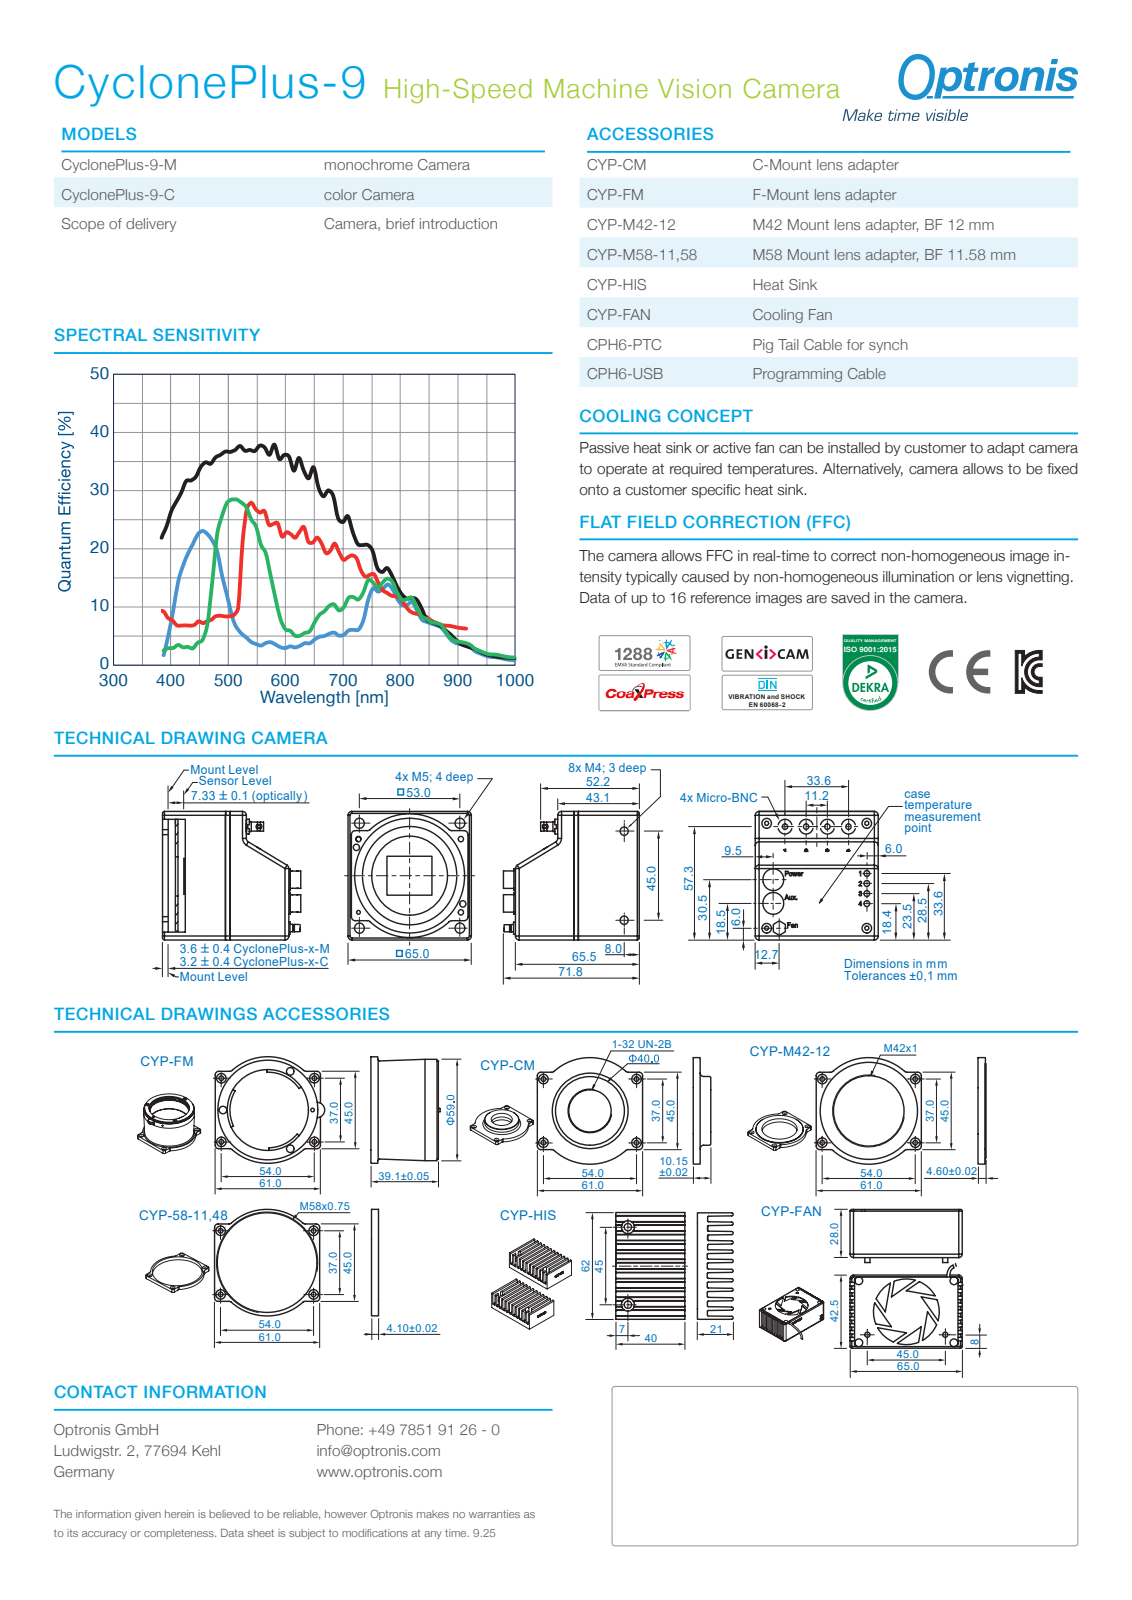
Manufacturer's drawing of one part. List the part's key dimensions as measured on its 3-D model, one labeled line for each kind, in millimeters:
Part name (STEP PRODUCT): 1200-MG-47_CycloneX_short
STEP written by: Autodesk Inventor 2026 (AUTOMOTIVE_DESIGN)
Units: millimetres
Bodies: 8 solids, 3121 faces (1553 planar, 986 cylindrical, 582 other)
Overall size (bounding box): 71.8 × 65 × 65
Volume: 71 233 mm³ · Surface area: 64 300 mm²
Round holes (diameter × count): ⌀0.8 ×18, ⌀0.5 ×10, ⌀1.57 ×8, ⌀2.7 ×8, ⌀0.45 ×4, ⌀0.46 ×4, ⌀2.01 ×4, ⌀2.2 ×4, ⌀3.05 ×4, ⌀3.24 ×4, ⌀3.59 ×4, ⌀4.2 ×4
Round bosses / shafts (diameter × count): ⌀1.1 ×10, ⌀7.5 ×4, ⌀6.32 ×4, ⌀5.2 ×4, ⌀4.55 ×4, ⌀4.5 ×4, ⌀3.8 ×4, ⌀3 ×4
Partial cylindrical surfaces — rounded edges, fillets, slot ends (radius × count): R0.2 ×58, R2 ×34, R3 ×34, R0.17 ×24, R1 ×20, R0.16 ×16, R0.45 ×10, R0.5 ×8
Main face-to-face distances: 2, 63, 65, 61, 28.1, 3, 2.9, 51, 30.6, 33.6
Hole centre spacings: 45.61, 45, 11.2, 8.02, 22.4, 8.62, 11.48, 25.99
